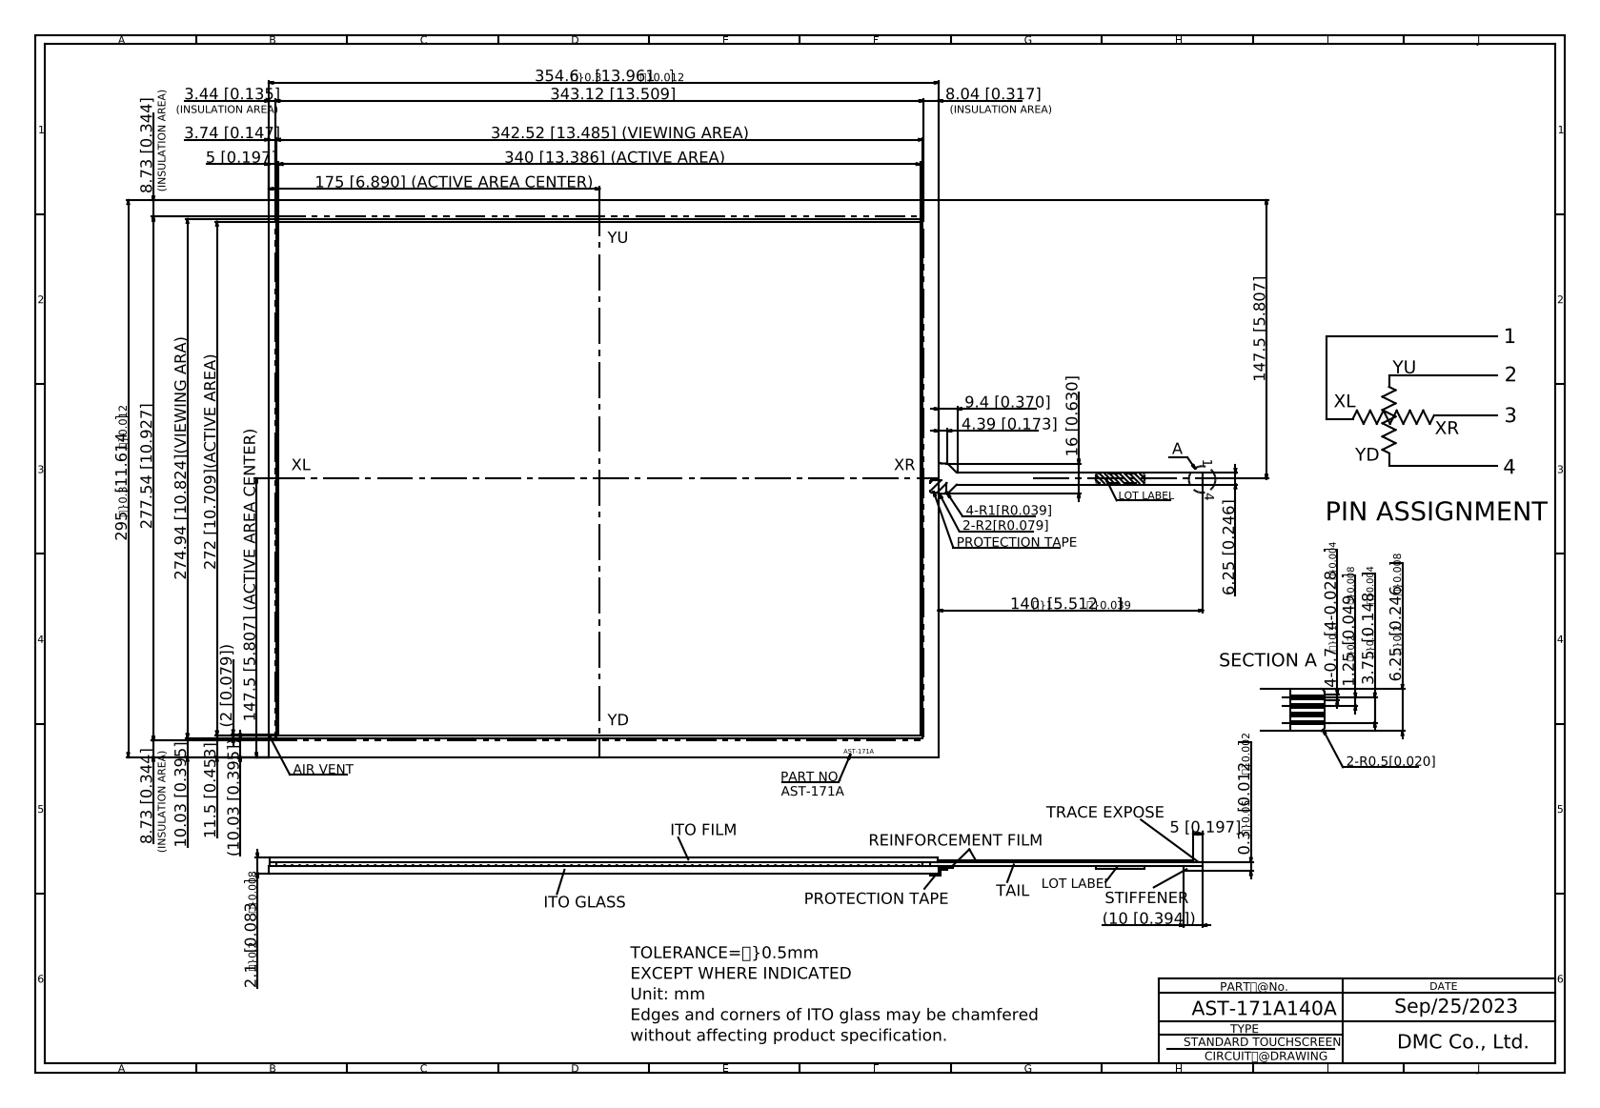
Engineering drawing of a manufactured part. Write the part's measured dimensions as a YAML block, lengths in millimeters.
part_name: "AST-171A140A"
step_written_by: "Autodesk Inventor 2020 (CONFIG_CONTROL_DESIGN)"
units: millimeters
bodies: {solids: 1, faces: 51, planar: 45, cylindrical: 6, other: 0}
overall_size: [565.52, 413, 2.1]
volume: 219618
surface_area: 214164
partial_cylinders:
  - {radius: 1, count: 4}
  - {radius: 0.5, count: 2}
face_to_face_distances: [2.1, 2, 1.9, 1.8, 295, 354.6, 10.03, 284.97, 11.5, 283.5]
